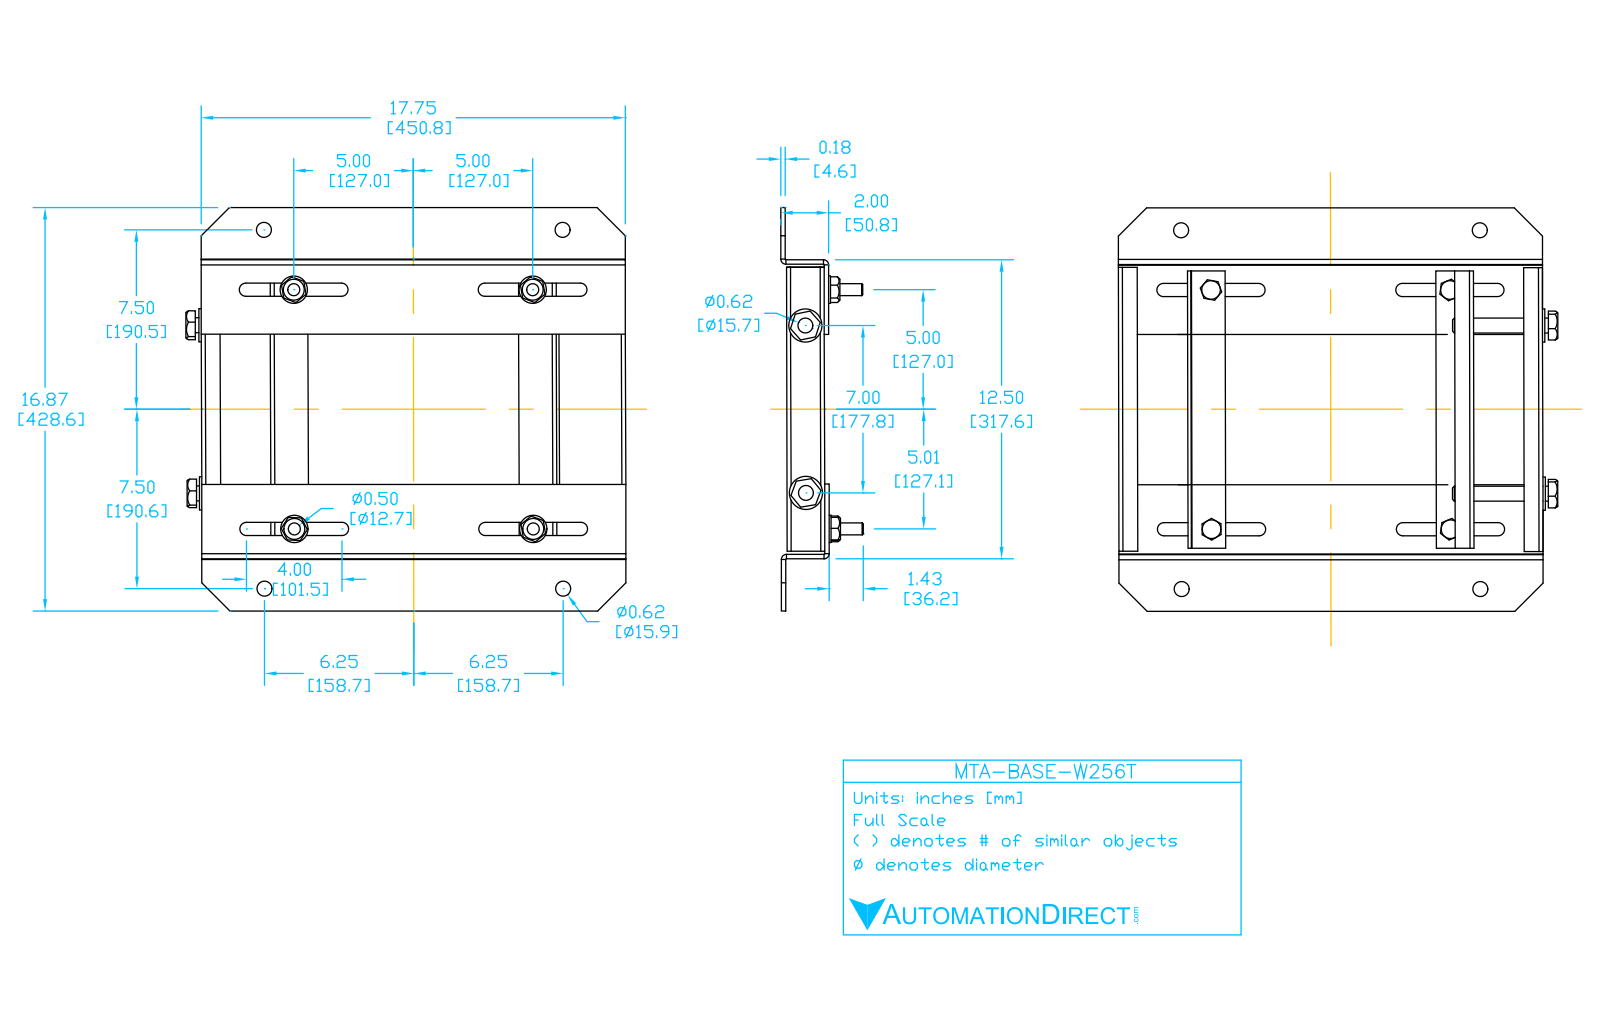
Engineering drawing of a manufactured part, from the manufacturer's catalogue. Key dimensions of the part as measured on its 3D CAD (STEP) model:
Part name (STEP PRODUCT): W256T
STEP written by: SolidWorks 2017 (AUTOMOTIVE_DESIGN)
Units: inches
Bodies: 26 solids, 398 faces (224 planar, 110 cylindrical, 64 other)
Overall size (bounding box): 18.163 × 16.87 × 3.427
Volume: 71.77 in³ · Surface area: 883.2 in²
Round holes (diameter × count): ⌀0.5 ×4, ⌀0.504 ×4, ⌀0.531 ×4, ⌀0.625 ×4, ⌀0.625 ×4, ⌀0.748 ×4, ⌀0.65 ×2
Round bosses / shafts (diameter × count): ⌀1.142 ×4, ⌀1.386 ×2, ⌀0.625 ×2
Partial cylindrical surfaces — rounded edges, fillets, slot ends (radius × count): R0.029 ×11, R0.276 ×8, R0.167 ×7, R0.214 ×4
Main face-to-face distances: 0.185, 1.815, 0.138, 2, 1.63, 12.315, 1.437, 0.323, 1.492, 1.677
Hole centre spacings: 10, 0.05, 7.008, 12.5, 14.142, 15, 19.526, 2.604
